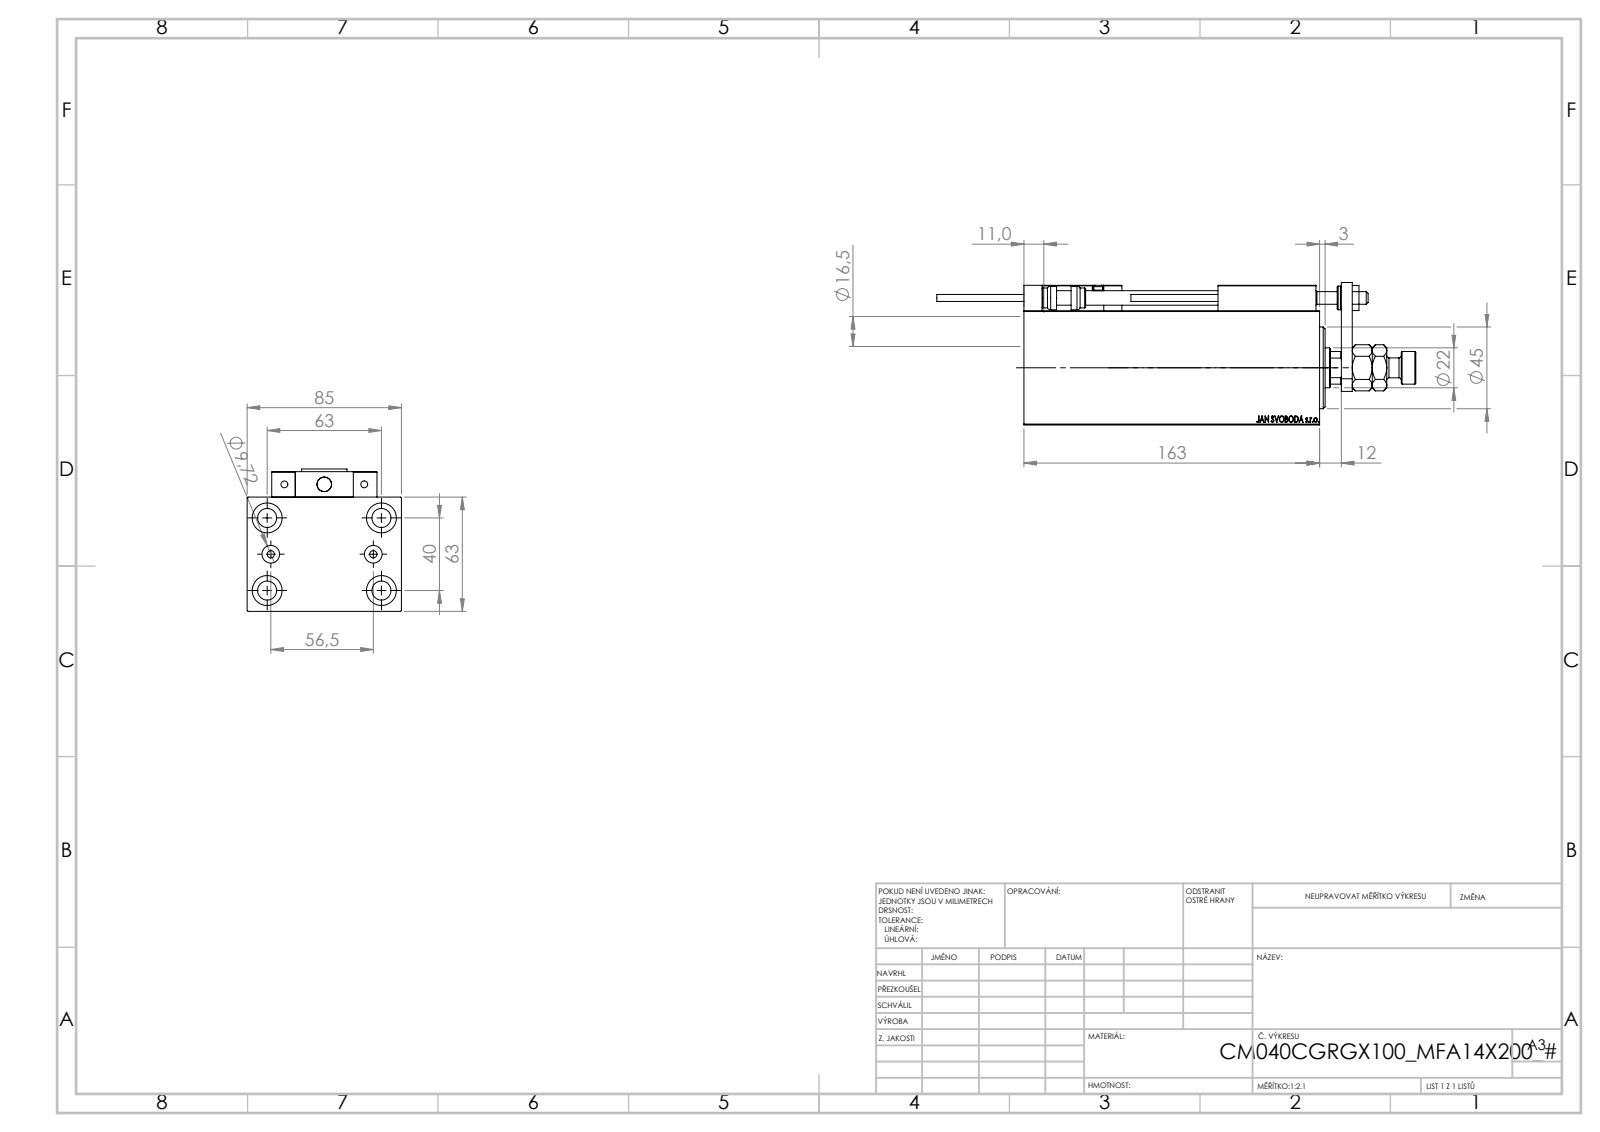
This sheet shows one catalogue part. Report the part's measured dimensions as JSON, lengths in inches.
{"part_name": "SWITCH X; ALLEN BOLT D8; SWITCH_X_FRONT_BACK; NUT_D12 (+8 more)", "step_written_by": "SolidWorks 2019 (CONFIG_CONTROL_DESIGN)", "units": "inches", "bodies": {"solids": 24, "faces": 1330, "planar": 576, "cylindrical": 188, "other": 566}, "overall_size": [10.394, 3.346, 3.091], "volume_in3": 47.62, "surface_area_in2": 242.8, "round_holes": [[0.157, 6], [0.315, 5], [0.65, 5], [0.126, 4], [0.413, 4], [0.197, 2], [0.383, 2], [0.276, 1], [0.492, 1], [0.866, 1], [1.004, 1], [1.575, 1]], "round_bosses_or_shafts": [[0.433, 2], [0.197, 2], [0.15, 2], [0.709, 1], [0.512, 1]], "partial_cylinders_radius": [[0.012, 30], [0.118, 2], [0.413, 1]], "face_to_face_distances": [2.48, 3.346, 0.472, 5.945, 6.417, 0.551, 0.709, 1.181, 3.031, 0.787], "hole_center_spacings": [1.469, 0.448, 0.787, 0.791, 0.807, 1.165, 1.169, 1.42]}
